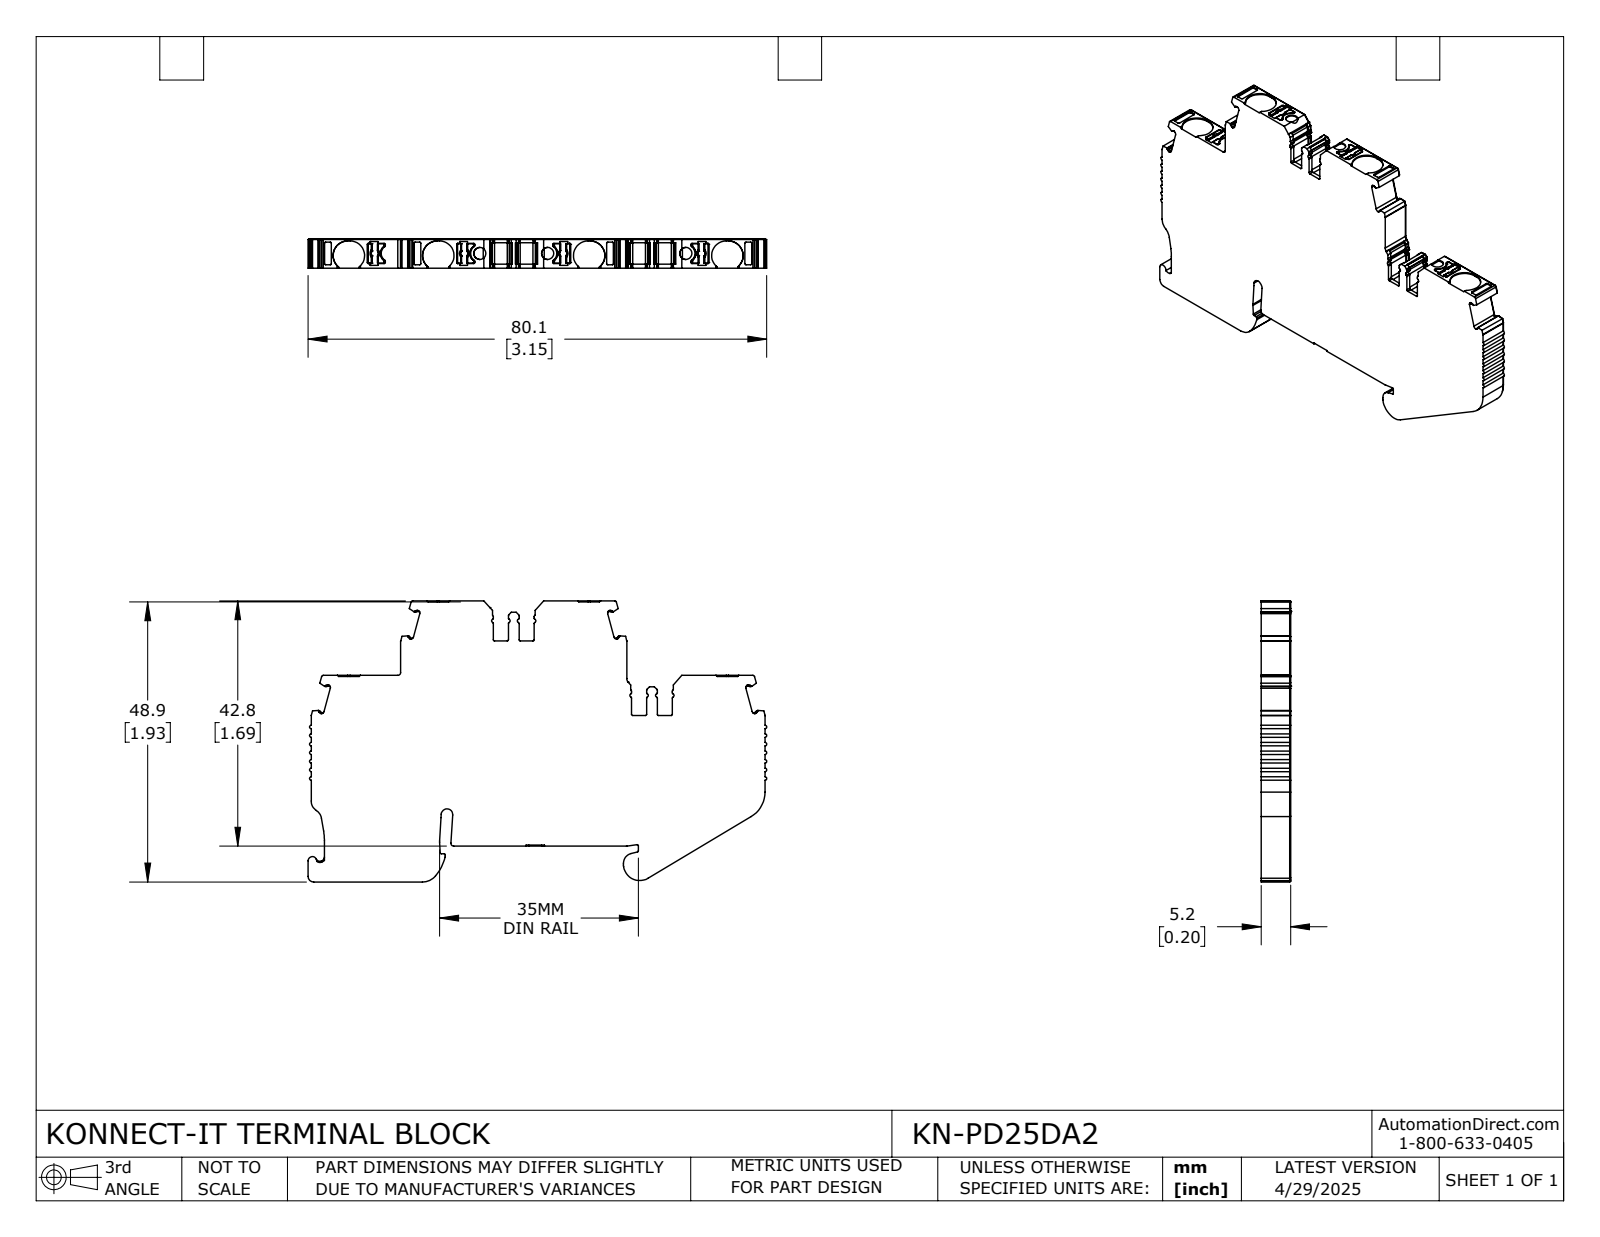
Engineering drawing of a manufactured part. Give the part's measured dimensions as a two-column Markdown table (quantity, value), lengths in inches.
| quantity | value |
| --- | --- |
| part name | KN-PD25DA2 |
| STEP written by | SolidWorks 2024 (CONFIG_CONTROL_DESIGN) |
| units | inches |
| bodies | 1 solid, 977 faces (472 planar, 438 cylindrical, 67 other) |
| overall size | 3.153 × 1.933 × 0.203 |
| volume | 0.889 in³ |
| surface area | 11.63 in² |
| round holes (diameter × count) | 0.083 × 3 |
| partial cylindrical surfaces (radius × count) | 0.008 × 100, 0.012 × 57, 0.004 × 41, 0.02 × 21, 0.016 × 17, 0.006 × 16, 0.024 × 9, 0.006 × 8 |
| main face-to-face distances | 0.203, 0.512, 0.246, 1.678, 1.166, 1.924, 0.079, 1.412, 0.504, 0.95 |
| hole center spacings | 0.466, 0.95, 1.417 |
